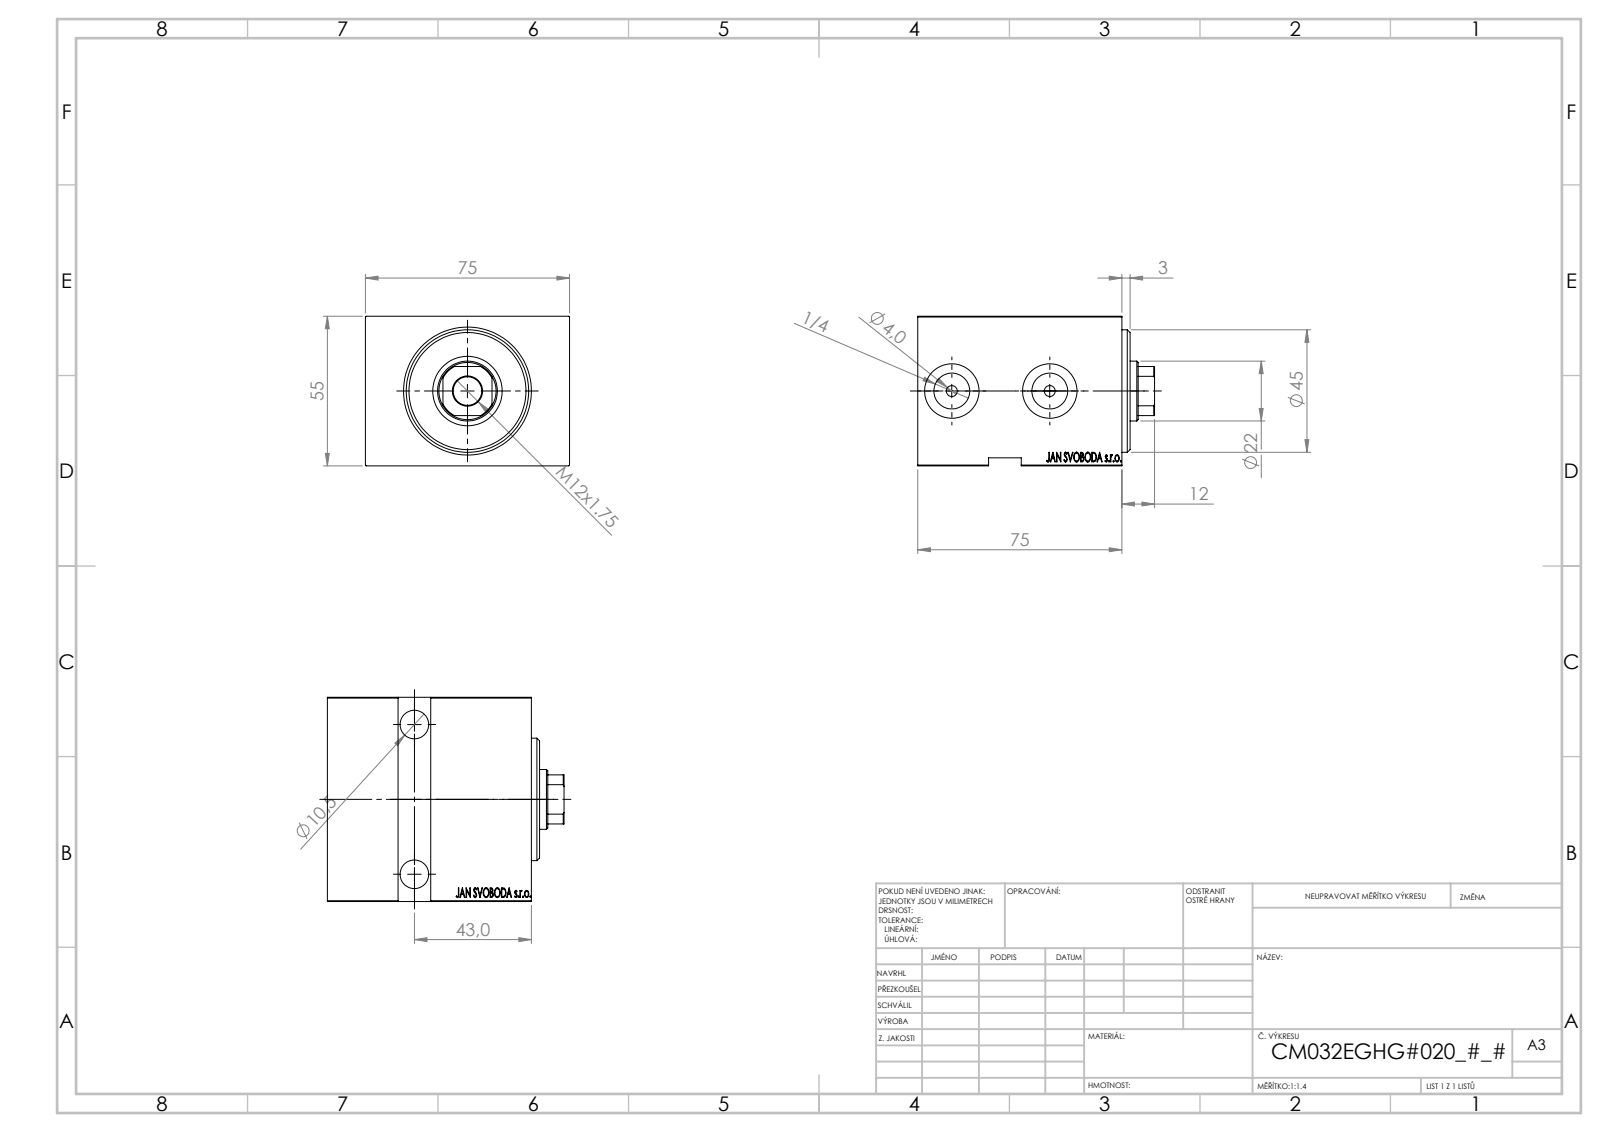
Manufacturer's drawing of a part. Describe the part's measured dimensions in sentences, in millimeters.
The part is named "V450CM_E_Body; V450CM_E_VCP; V450CM_VC_B". Its 3-D file was written by "SolidWorks 2019 (CONFIG_CONTROL_DESIGN)". It is 3 solids with 846 faces: 408 planar, 44 cylindrical and 394 other. Overall it measures 87 by 75 by 55 millimeters. Its volume is 282 829 cubic millimeters and its surface area 54 109 square millimeters. Round holes: 3 of diameter 10.5, 2 of diameter 4, 2 of diameter 13.16, 2 of diameter 16.5, 2 of diameter 20, 1 of diameter 22, 1 of diameter 25.5, 1 of diameter 32, 1 of diameter 34, 1 of diameter 45. Partial cylindrical surfaces (rounded edges, fillets, slot ends): 1 of radius 10.5. The main face-to-face distances are 75, 55, 3, 65, 10, 5, 70, 60, 8, 52. The hole center spacings are 36, 55.
